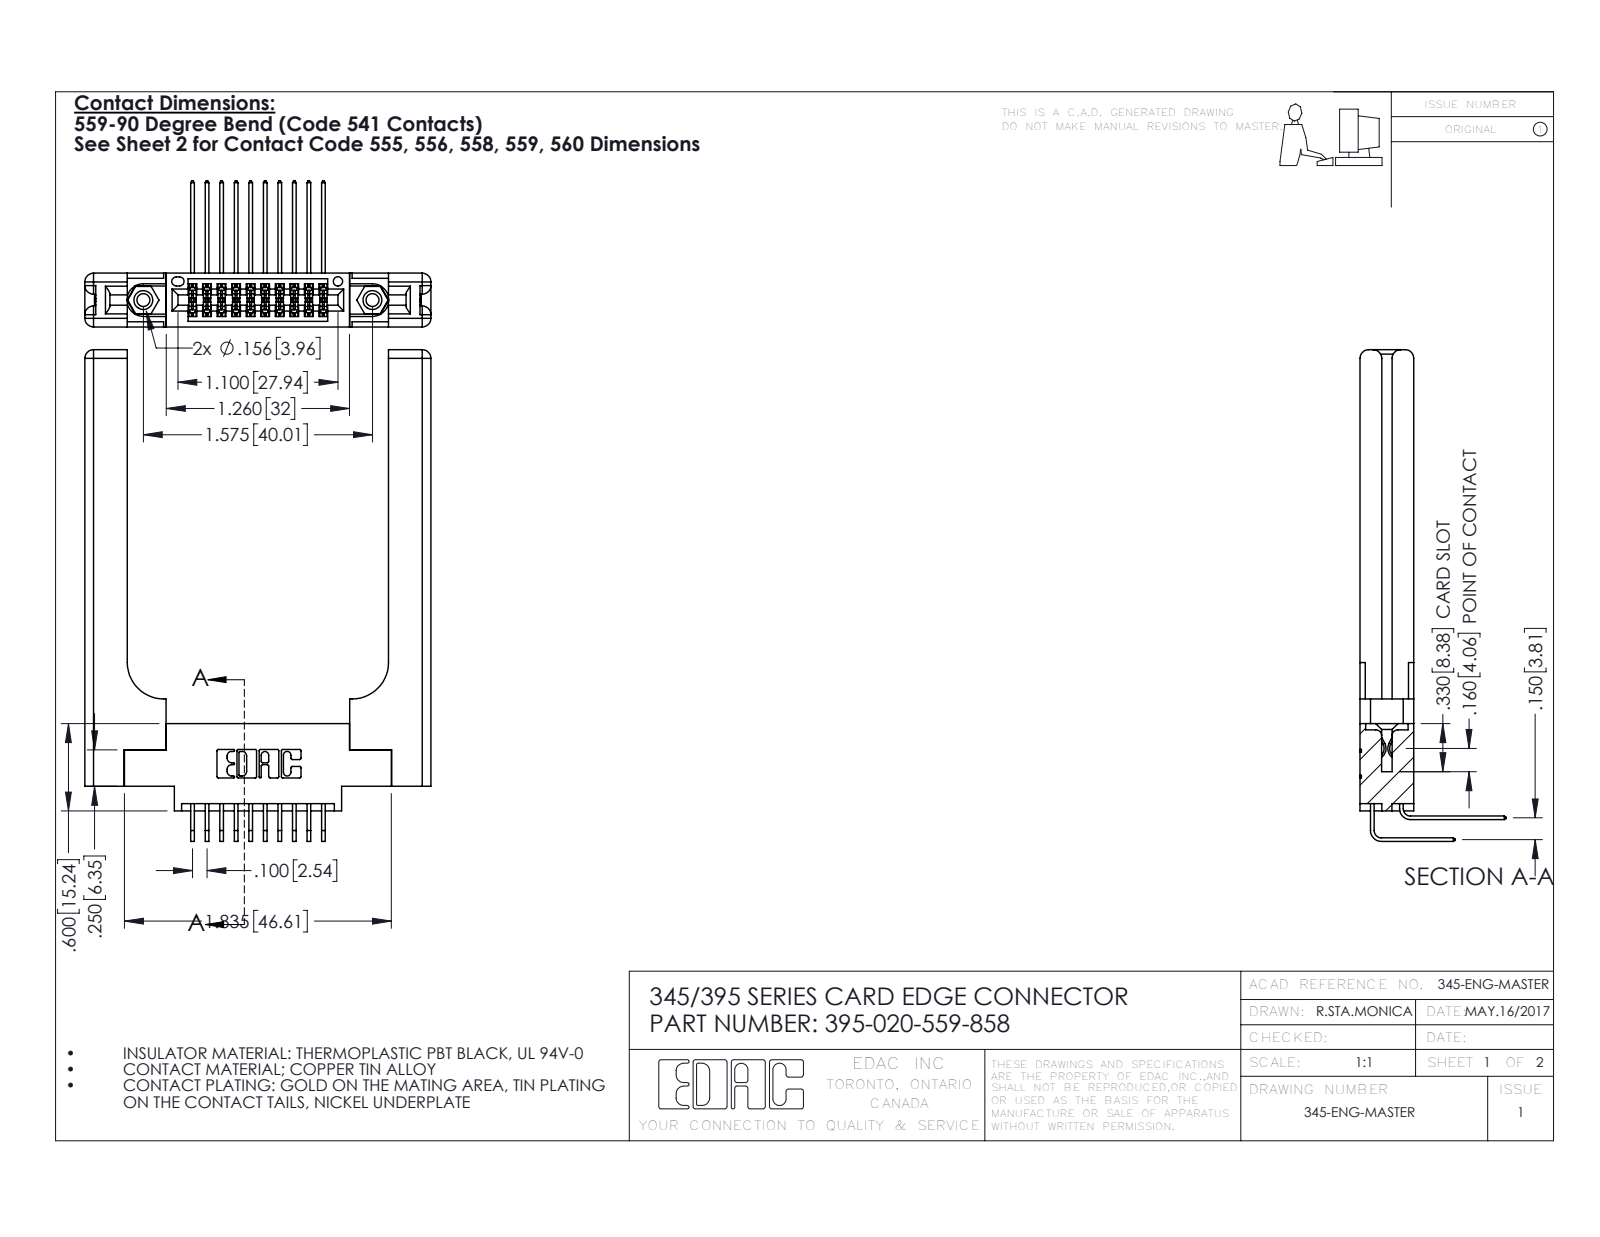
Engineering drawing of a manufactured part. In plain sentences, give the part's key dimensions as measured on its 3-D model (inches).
The part is named "345 Part_0.170 Offset - 0.156 Dia-TH; 345-292-001_558 559 Tail - 1; 345-250-001_345-250-001-102; 395-020-559-858 (+2 more)". Its 3-D file was written by "SolidWorks 2016 (CONFIG_CONTROL_DESIGN)". It is 25 solids with 1426 faces: 932 planar, 434 cylindrical and 60 other. Overall it measures 3.379 by 2.379 by 1.005 inches. Its volume is 0.857 cubic inches and its surface area 20.72 square inches. Round holes: 2 of diameter 0.089, 2 of diameter 0.125, 2 of diameter 0.156, 1 of diameter 0.064. Round bosses or shafts: 2 of diameter 0.155. Partial cylindrical surfaces (rounded edges, fillets, slot ends): 31 of radius 0.006, 22 of radius 0.01, 16 of radius 0.06, 6 of radius 0.007, 6 of radius 0.031, 3 of radius 0.026, 2 of radius 0.014, 2 of radius 0.019. The main face-to-face distances are 0.37, 0.072, 0.15, 0.148, 0.077, 0.22, 0.298, 1.796, 0.225, 0.12. The hole center spacings are 0.27, 1.344, 1.575.
